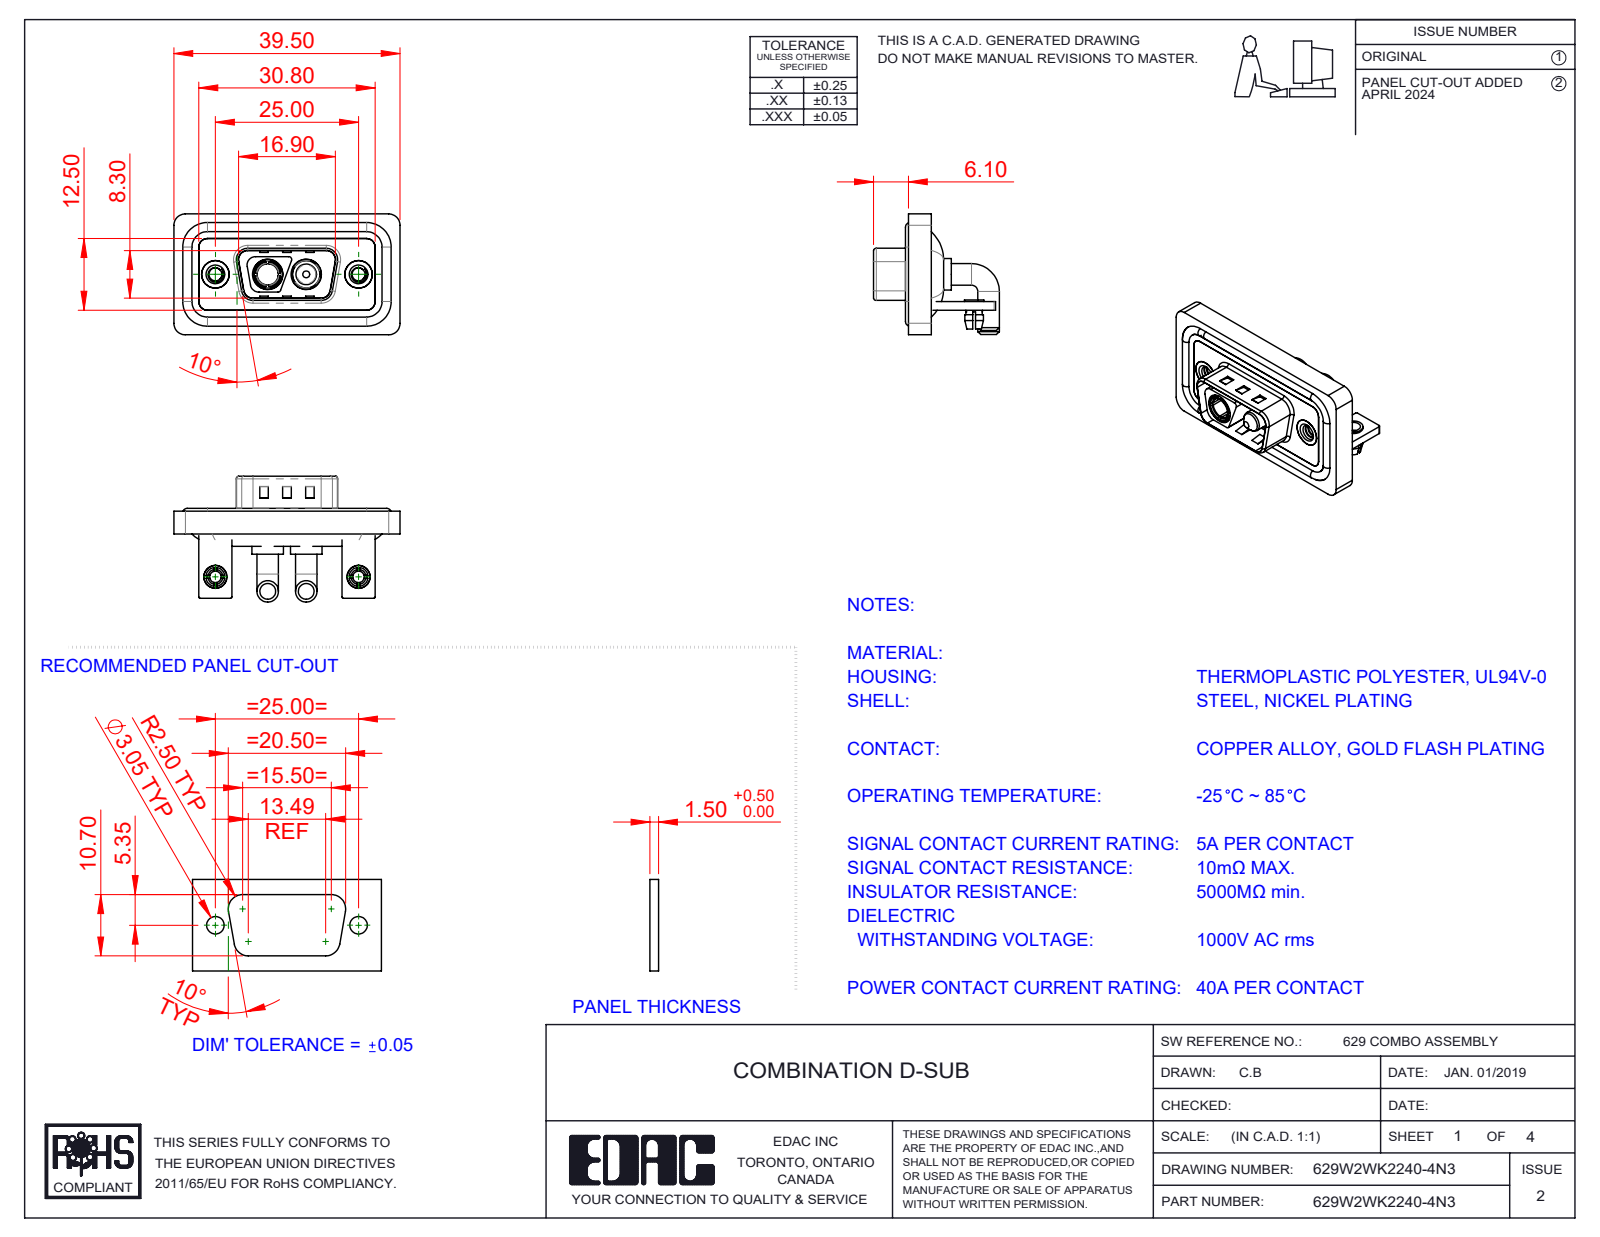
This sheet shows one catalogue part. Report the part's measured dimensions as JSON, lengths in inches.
{"part_name": "629Combo Board Lock; 629Combo Shell Front_09 Contacts; 629Combo Threaded Rivet_3; Power Pin_40A RA (+6 more)", "step_written_by": "SolidWorks 2023 (CONFIG_CONTROL_DESIGN)", "units": "inches", "bodies": {"solids": 15, "faces": 674, "planar": 257, "cylindrical": 281, "other": 136}, "overall_size": [1.555, 0.865, 0.831], "volume_in3": 0.314, "surface_area_in2": 13.05, "round_holes": [[0.079, 2], [0.089, 2], [0.098, 2], [0.126, 2], [0.157, 2], [0.189, 2], [0.191, 2], [0.197, 2], [0.209, 2], [0.146, 1]], "round_bosses_or_shafts": [[0.148, 4], [0.063, 4], [0.217, 2], [0.205, 2], [0.193, 2], [0.187, 2], [0.157, 2], [0.134, 2]], "partial_cylinders_radius": [[0.059, 20], [0.079, 19], [0.01, 16], [0.02, 11], [0.063, 8], [0.024, 4], [0.026, 4], [0.035, 4]], "face_to_face_distances": [0.016, 0.059, 0.114, 0.031, 0.043, 0.047, 0.083, 0.063, 0.146, 0.098], "hole_center_spacings": [0.36, 0.624, 0.984, 0.265]}
